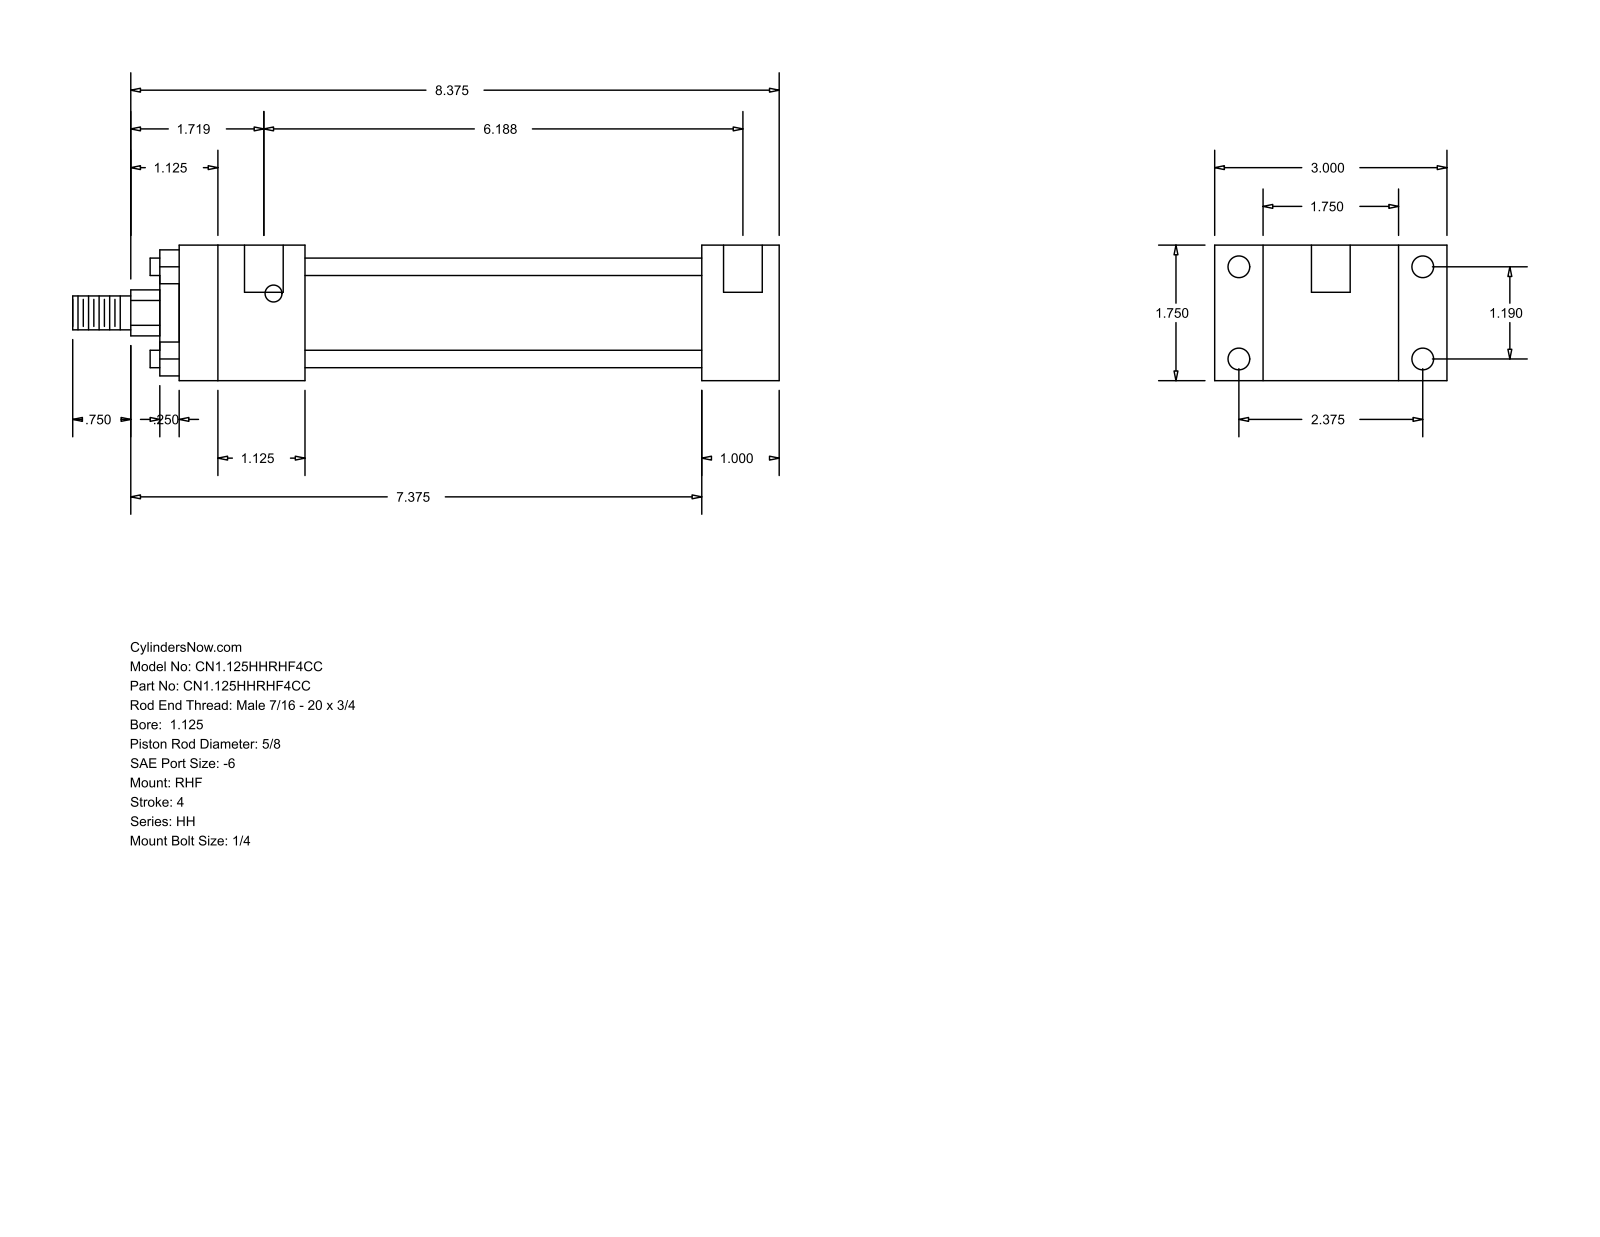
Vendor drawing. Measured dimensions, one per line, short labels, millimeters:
name: HH_RHF__0112_0.625
written by: GSSL Pune (CONFIG_CONTROL_DESIGN)
unit: mm
bodies: 0 solids, 88 faces (60 planar, 28 cylindrical, 0 other)
size: 231.78 × 76.2 × 44.45
holes: 4× ⌀5.56, 4× ⌀7.14, 2× ⌀12.7
bosses: 4× ⌀5.71, 1× ⌀34.92, 1× ⌀28.57, 1× ⌀15.88, 1× ⌀11.11
rounds: 1× R7.54
face distances: 44.46, 15.87, 25.4, 60.33, 76.2, 130.17, 155.57, 41.27, 171.44, 196.84
hole spacings: 30.22, 60.32, 67.47, 153.99, 3.17, 157.16
